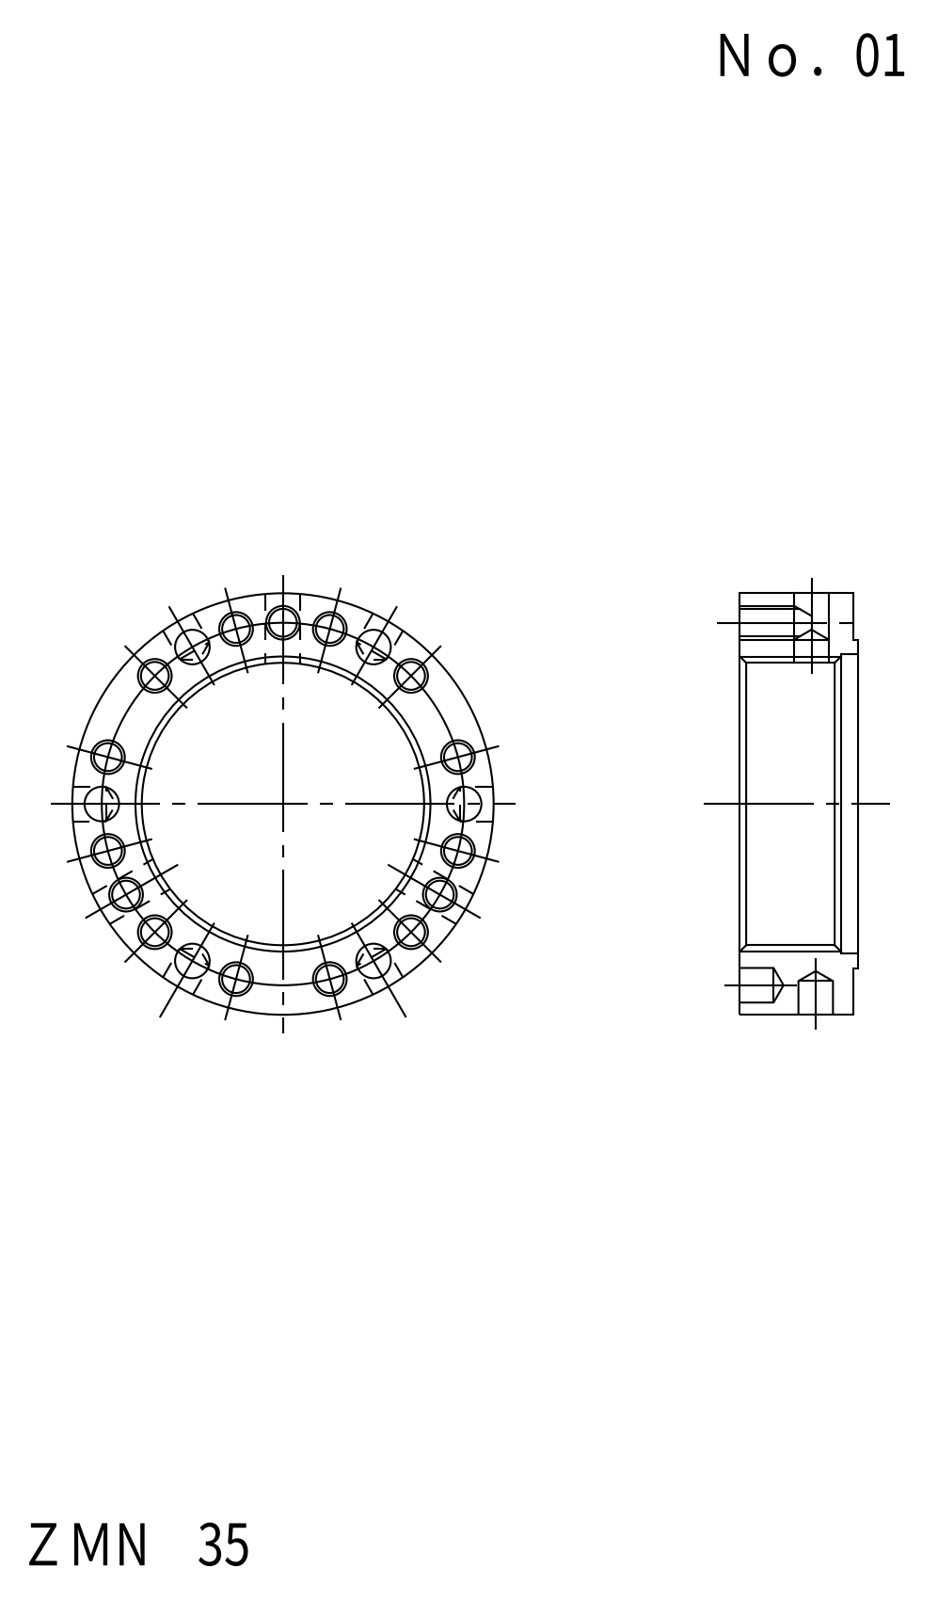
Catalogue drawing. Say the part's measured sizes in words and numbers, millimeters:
The part is named "FKD ZMN35". Its 3-D file was written by "Autodesk Inventor LT (CONFIG_CONTROL_DESIGN)". It is 1 solid with 62 faces: 4 planar, 34 cylindrical and 24 other. Overall it measures 50 by 50 by 14 millimeters. Its volume is 11 561 cubic millimeters and its surface area 7 791 square millimeters. Round holes: 15 of diameter 3.24, 12 of diameter 4.1, 1 of diameter 35, 1 of diameter 35.5. Round bosses or shafts: 1 of diameter 50, 1 of diameter 39. The main face-to-face distances are 13.5, 0.5, 14, 1.5, 1, 12.5. The hole center spacings are 21.5, 37.24, 42.63, 11.13, 30.41, 5.61, 16.45, 26.17.
